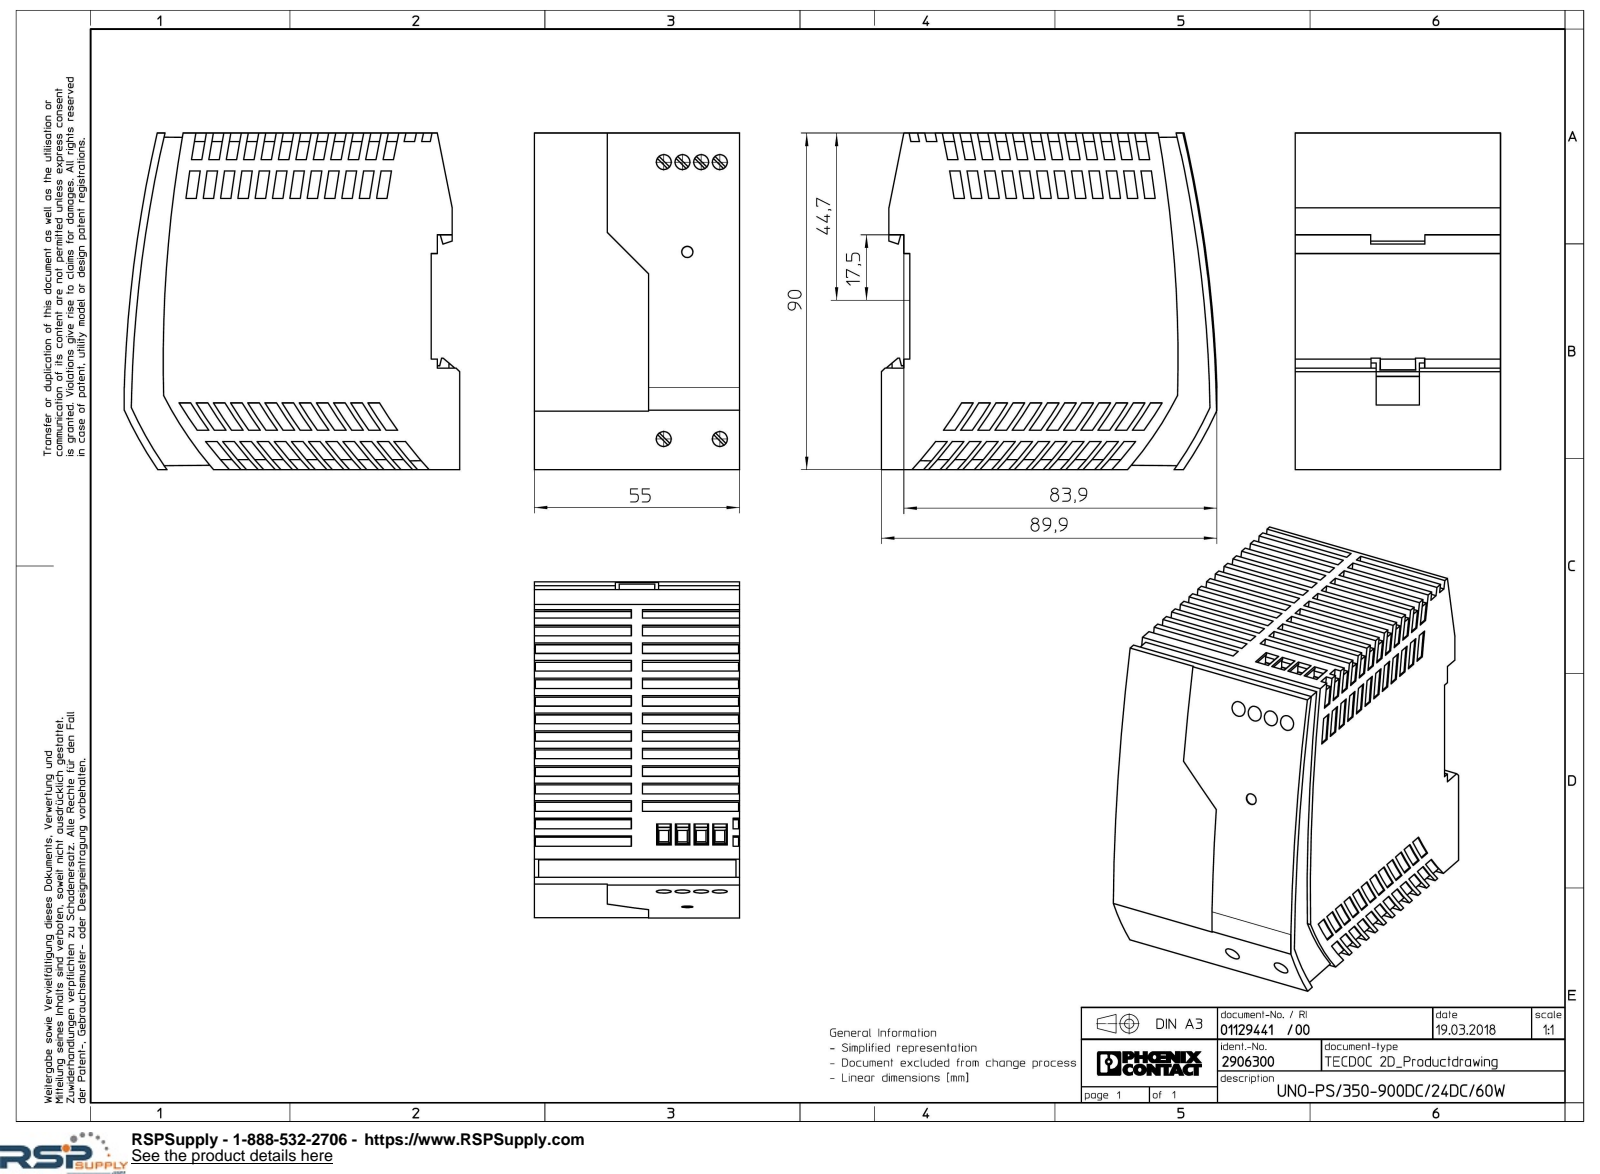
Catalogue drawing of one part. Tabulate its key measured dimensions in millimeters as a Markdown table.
| quantity | value |
| --- | --- |
| part name | UNO_PS_350_900DC_24DC_60W-select |
| STEP written by | Creo Elements/Direct Modeling 18.1I 14-Aug-2016 (C) Parametric Technology GmbH (AUTOMOTIVE_DESIGN) |
| units | millimeters |
| bodies | 1 solid, 779 faces (558 planar, 219 cylindrical, 2 other) |
| overall size | 90 × 89.87 × 55 |
| volume | 395 571 mm³ |
| surface area | 43 992 mm² |
| round holes (diameter × count) | 4 × 6 |
| partial cylindrical surfaces (radius × count) | 111 × 26, 98 × 1, 98.55 × 1, 100 × 1, 282.66 × 1, 284.9 × 1, 286.76 × 1, 291.36 × 1 |
| main face-to-face distances | 55, 2.3, 87.7, 90, 2.7, 85, 87.3, 54.7, 7.6, 54.4 |
| hole center spacings | 5, 10, 74, 74.17, 15, 15.03, 74.67, 74.68 |
